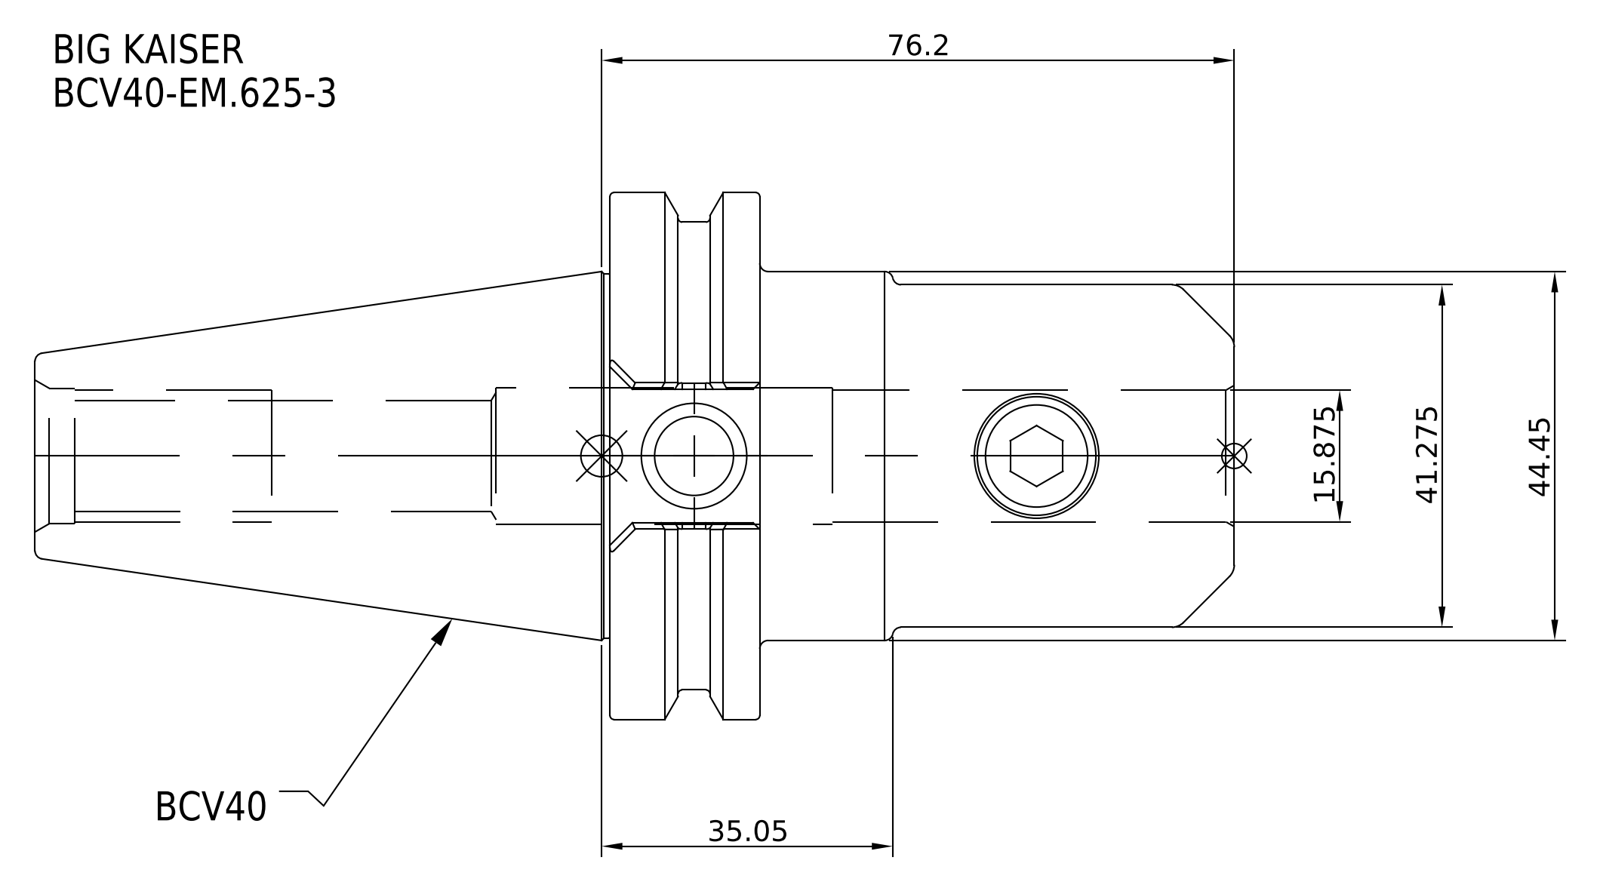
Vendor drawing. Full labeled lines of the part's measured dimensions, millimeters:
Part name (STEP PRODUCT): BCV40-EM_625-3
STEP written by: SolidWorks 2021 (CONFIG_CONTROL_DESIGN)
Units: millimetres
Bodies: 1 solid, 30 faces (8 planar, 14 cylindrical, 8 other)
Overall size (bounding box): 144.45 × 63.5 × 63.5
Volume: 189 976 mm³ · Surface area: 26 309 mm²
Round holes (diameter × count): ⌀15.88 ×1
Round bosses / shafts (diameter × count): ⌀63.5 ×1, ⌀56.36 ×1, ⌀44.45 ×1, ⌀41.27 ×1
Main face-to-face distances: 18.05, 87.3, 69.25, 57.15, 75.2, 144.45, 41.15, 16, 34.05, 103.3
